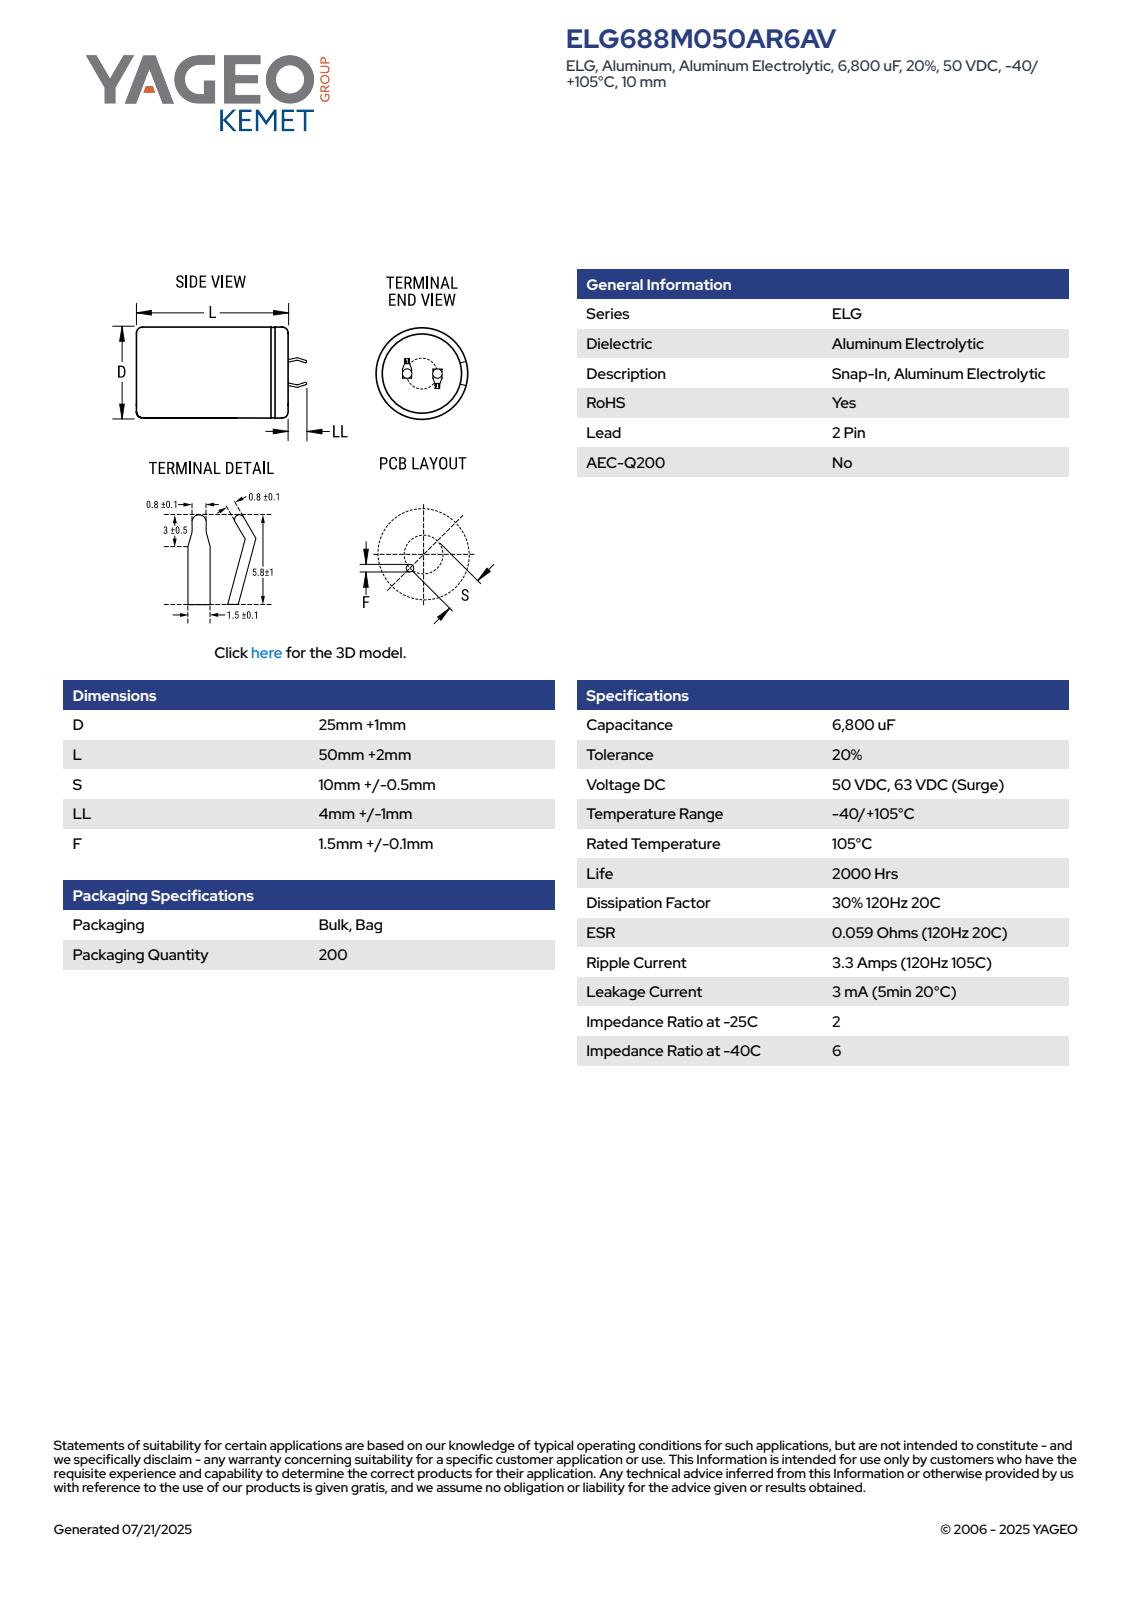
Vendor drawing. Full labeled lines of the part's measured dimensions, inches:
Part name (STEP PRODUCT): CARS_K2P_25X50_D26L52S10LL5F1.6
STEP written by: SolidWorks 2014 (AUTOMOTIVE_DESIGN)
Units: inches
Bodies: 1 solid, 100 faces (52 planar, 9 cylindrical, 39 other)
Overall size (bounding box): 2.244 × 1.024 × 1.024
Volume: 1.673 in³ · Surface area: 8.244 in²
Round holes (diameter × count): ⌀0.906 ×1
Round bosses / shafts (diameter × count): ⌀1.024 ×1
Partial cylindrical surfaces — rounded edges, fillets, slot ends (radius × count): R0.511 ×1
Main face-to-face distances: 2.047, 2.067, 0.02, 0.279, 0.024, 0.023, 0.299, 0.03, 0.053, 0.302
